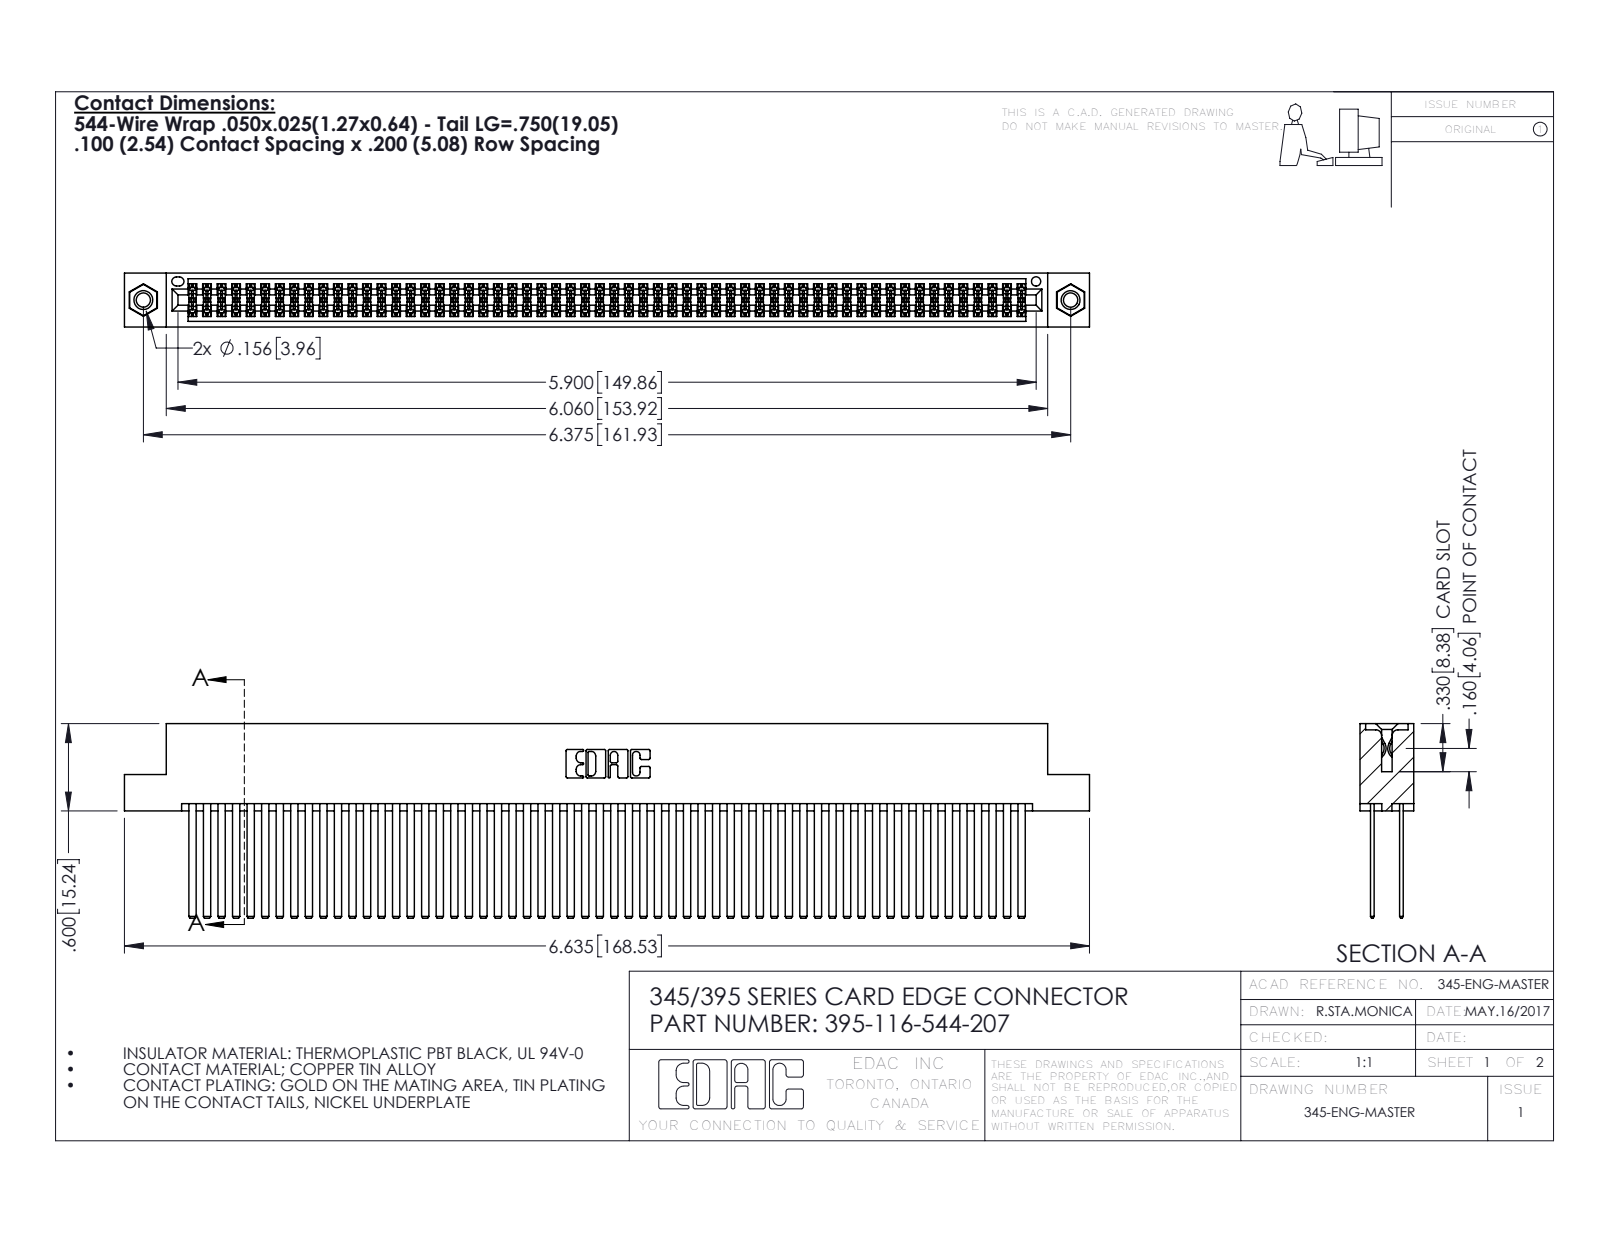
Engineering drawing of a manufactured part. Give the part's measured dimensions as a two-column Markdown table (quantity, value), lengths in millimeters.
| quantity | value |
| --- | --- |
| part name | 345 Part_Flush Mounting Lugs - 0.156 Dia-TI; 395-116-544-207; 345-292-001_345-293-144; 345-250-001_345-250-005-103 |
| STEP written by | SolidWorks 2016 (CONFIG_CONTROL_DESIGN) |
| units | millimeters |
| bodies | 119 solids, 5290 faces (3476 planar, 1798 cylindrical, 16 other) |
| overall size | 168.5 × 34 × 9.4 |
| volume | 18 120 mm³ |
| surface area | 31 900 mm² |
| round holes (diameter × count) | 2.5 × 2, 3.2 × 2, 4 × 2, 1.6 × 1 |
| round bosses / shafts (diameter × count) | 3.9 × 2 |
| partial cylindrical surfaces (radius × count) | 0.2 × 174, 0.3 × 22, 0.2 × 6, 0.8 × 6, 0.7 × 3, 0.4 × 2, 0.5 × 2, 0.6 × 2 |
| main face-to-face distances | 5.1, 0.6, 1.8, 2.5, 6.9, 7.6, 5.7, 4.4, 9.4, 1.3 |
| hole center spacings | 6.9, 155.9, 161.9 |
